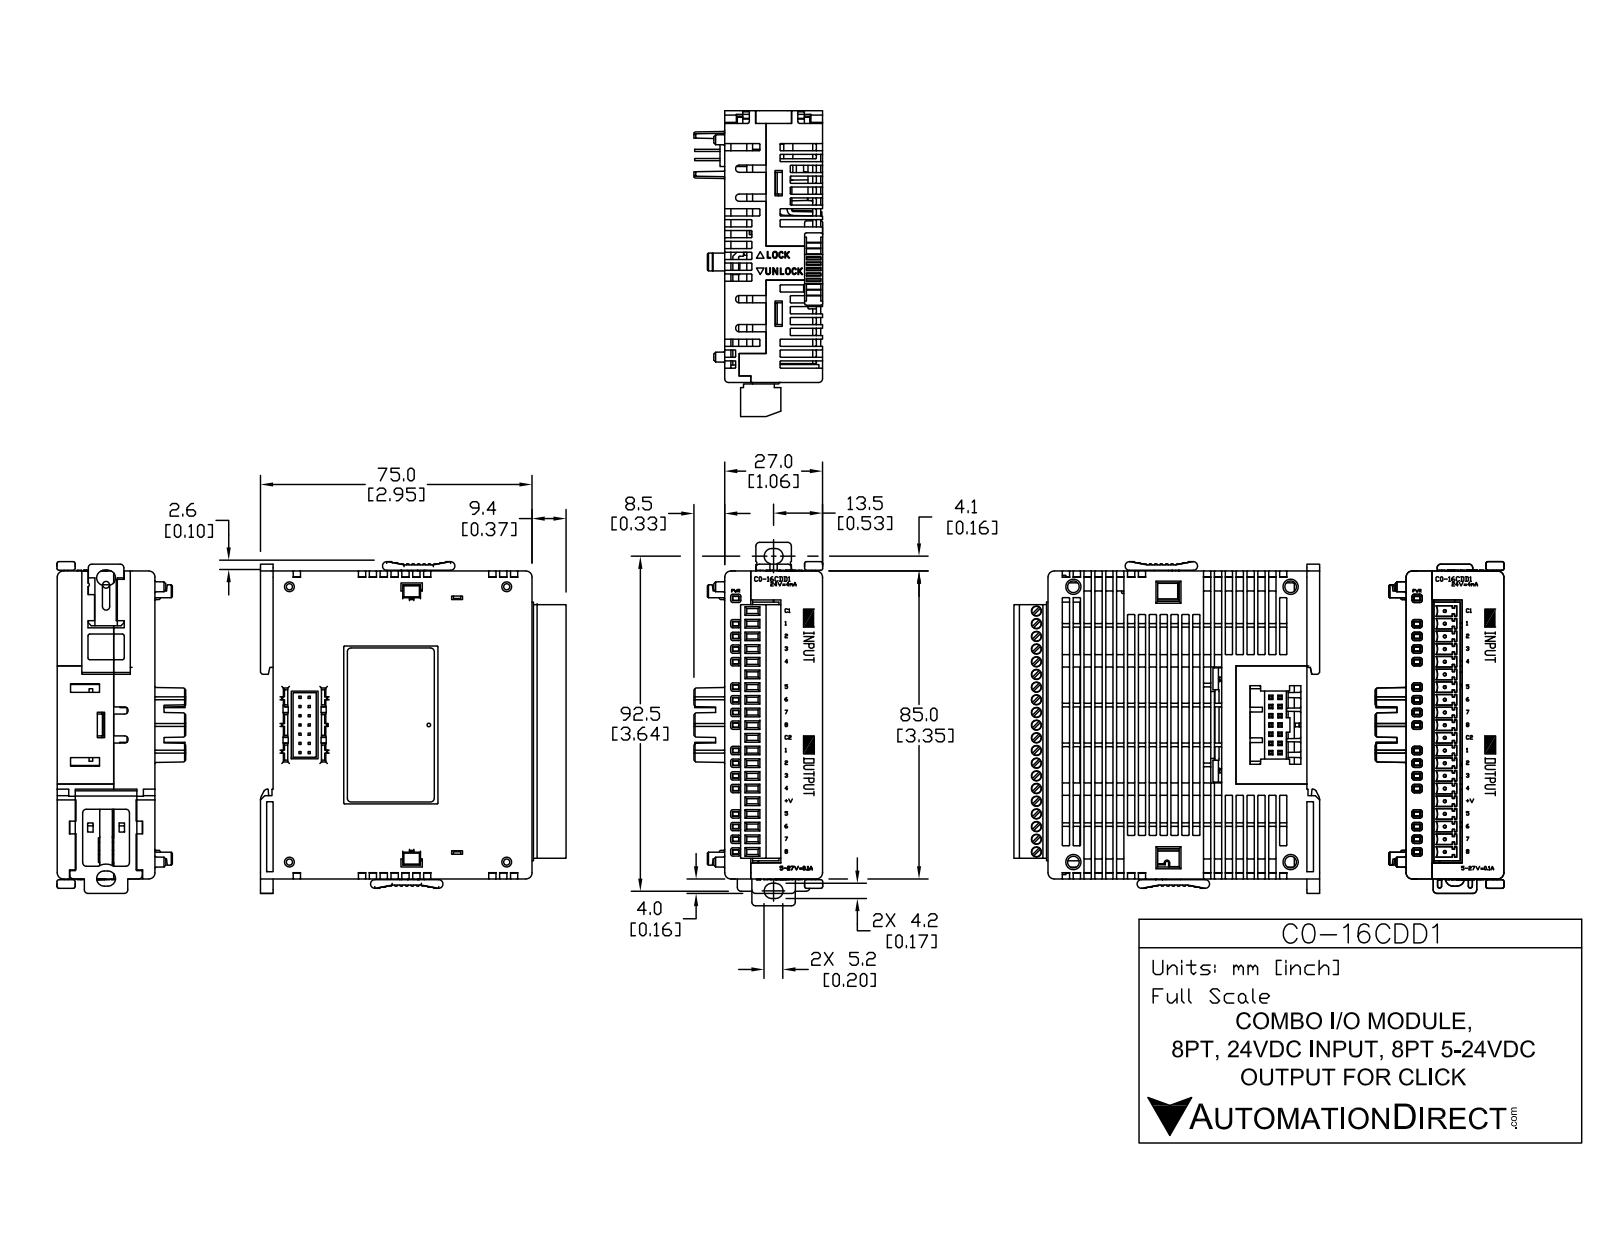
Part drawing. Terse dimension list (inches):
name: C0-16CDD1
written by: SolidWorks 2017 (AUTOMOTIVE_DESIGN)
unit: in
bodies: 1 solid, 4087 faces (2884 planar, 1037 cylindrical, 166 other)
size: 3.606 × 3.323 × 1.4
volume: 10.07 in³; area: 52.13 in²
holes: 20× ⌀0.039, 20× ⌀0.11, 4× ⌀0.126, 2× ⌀0.079
bosses: 20× ⌀0.102, 1× ⌀0.075
rounds: 570× R0.008, 43× R0.02, 22× R0.012, 20× R0.11, 18× R0.039, 12× R0.047, 6× R0.067, 4× R0.083
face distances: 0.02, 1.063, 0.02, 1.043, 2.815, 3.346, 0.067, 1.035, 1.056, 0.138
hole spacings: 0.138, 0.276, 0.413, 0.551, 0.689, 0.827, 0.965, 1.102
